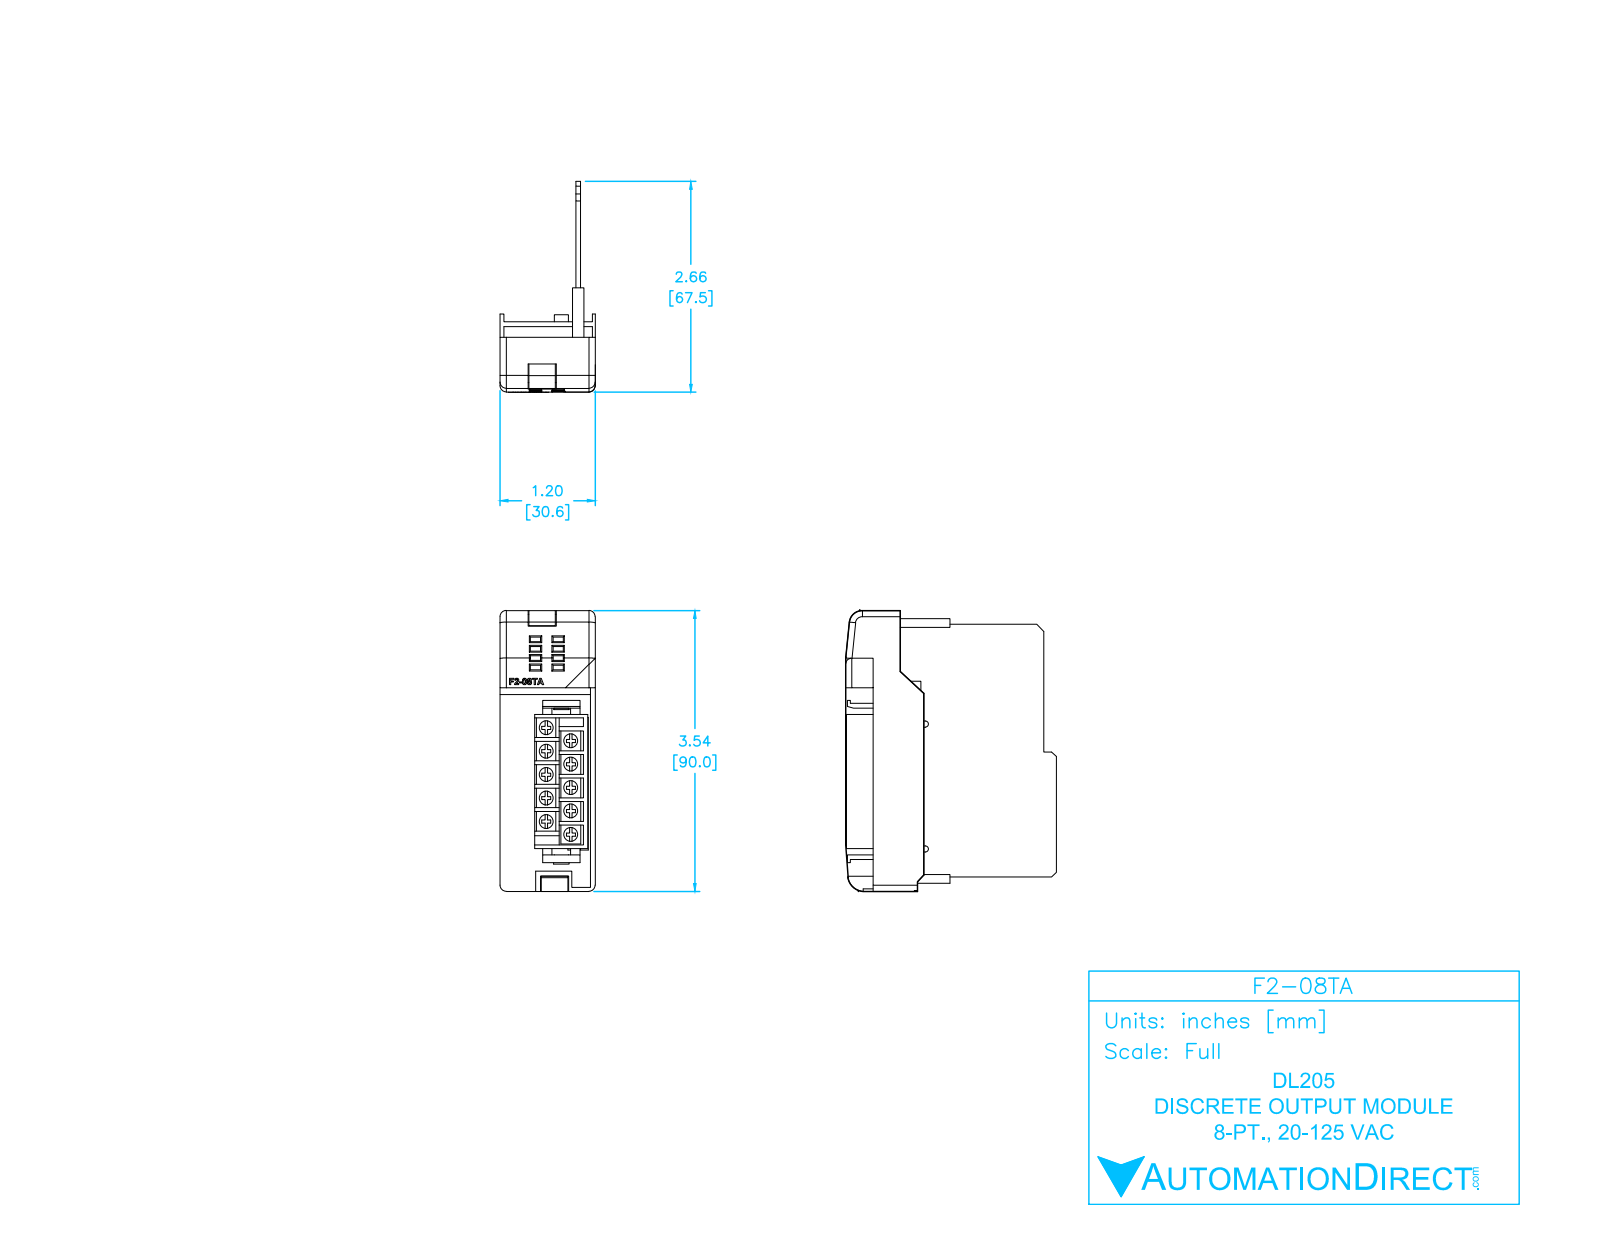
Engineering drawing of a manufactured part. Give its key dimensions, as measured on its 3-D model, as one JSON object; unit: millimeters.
{"part_name": "F2-08TA_ModuleCase_lightNEW", "step_written_by": "SolidWorks 2009 (AUTOMOTIVE_DESIGN)", "units": "millimeters", "bodies": {"solids": 6, "faces": 558, "planar": 402, "cylindrical": 75, "other": 81}, "overall_size": [90, 67.61, 30.55], "volume_mm3": 25374, "surface_area_mm2": 28531, "round_bosses_or_shafts": [[4.5, 10]], "partial_cylinders_radius": [[0.35, 16], [2, 9], [0.25, 2], [1, 2], [1.25, 2], [4.12, 1], [5.39, 1]], "face_to_face_distances": [1.5, 4.72, 6.22, 2.37, 3.87, 2.35, 3.22, 0.85, 7.25, 8.14]}
